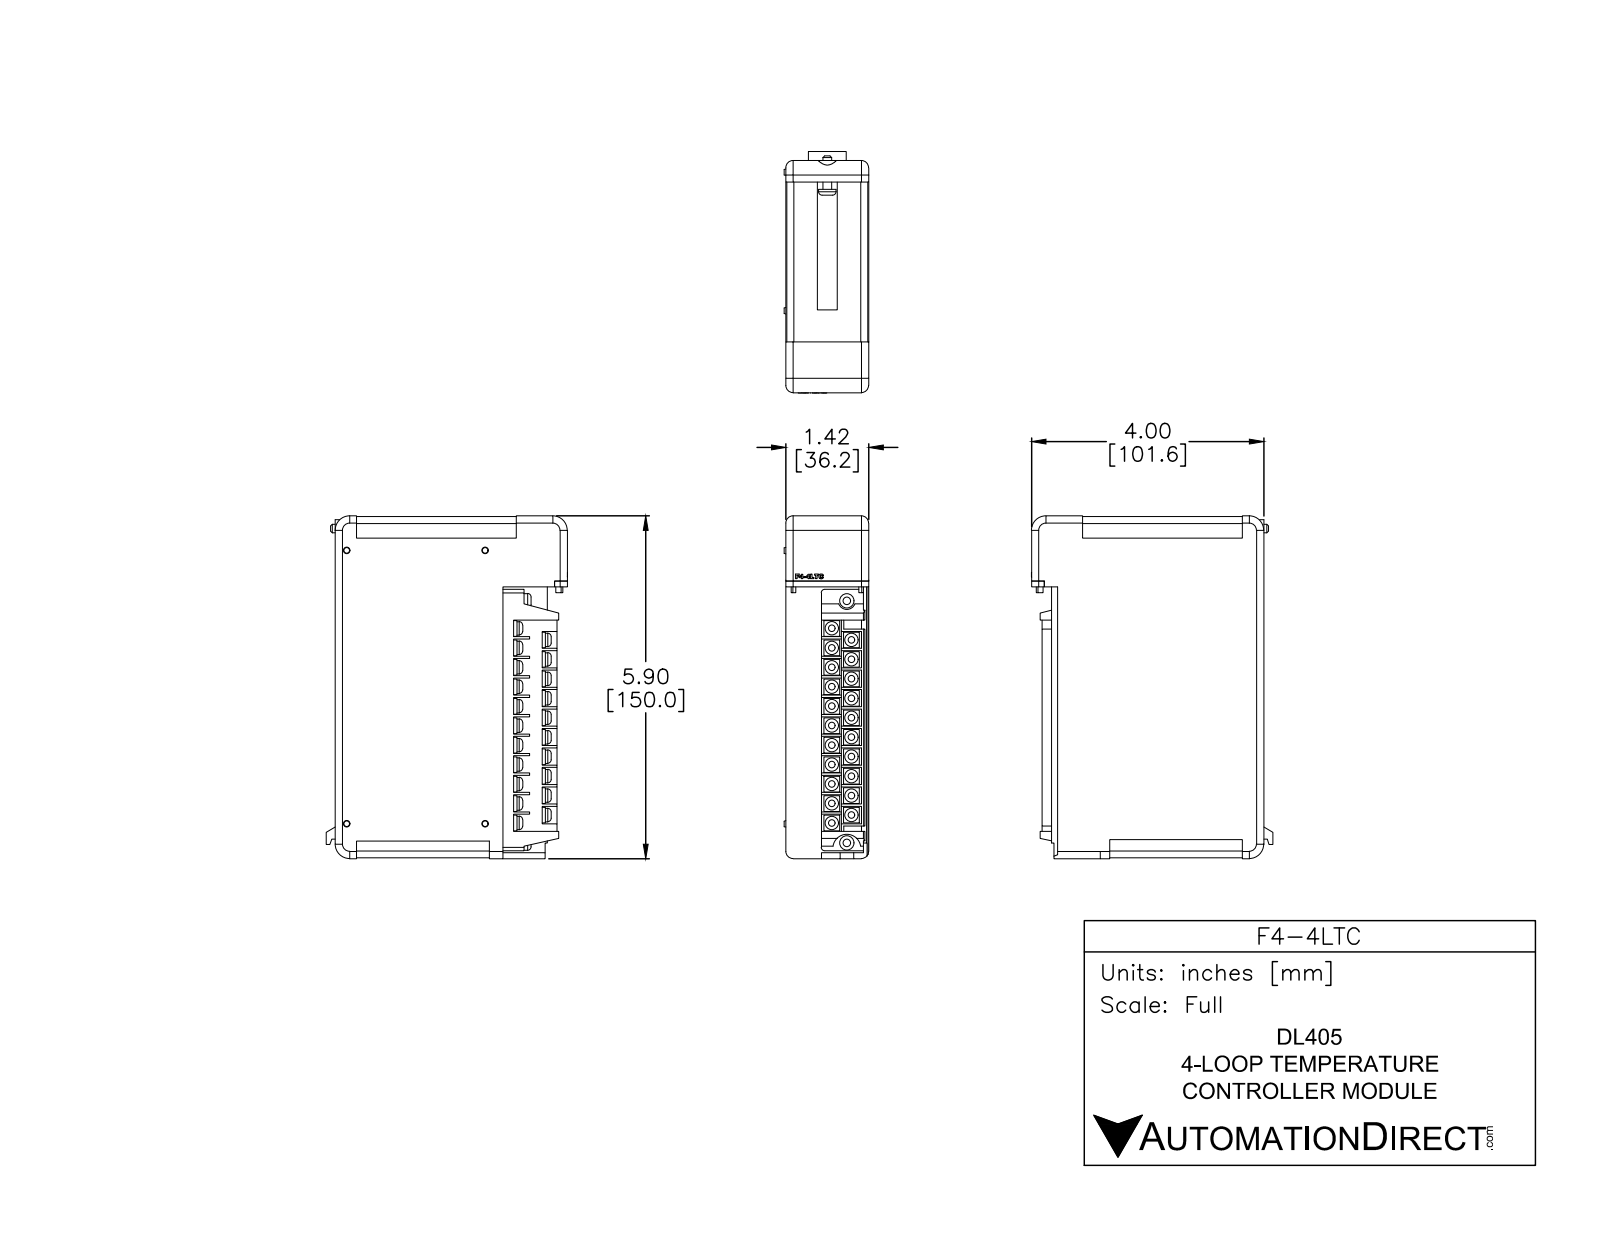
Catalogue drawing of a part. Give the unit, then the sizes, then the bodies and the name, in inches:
Units: inches
Overall size (bounding box): 5.905 × 4.156 × 1.455
Round bosses / shafts (diameter × count): ⌀0.23 ×21, ⌀0.25 ×2, ⌀0.3 ×1, ⌀0.15 ×1
Partial cylindrical surfaces — rounded edges, fillets, slot ends (radius × count): R0.125 ×8, R0.12 ×4, R0.25 ×3, R0.015 ×2, R0.03 ×2, R0.06 ×2, R0.149 ×1, R0.151 ×1
Main face-to-face distances: 1.425, 0.015, 2.89, 5.875, 1.41, 0.47, 0.2, 0.955, 5.89, 1.21
Volume: 27.51 in³ · Surface area: 86.81 in²
Bodies: 13 solids, 576 faces (418 planar, 86 cylindrical, 72 other)
Part name (STEP PRODUCT): F4--4LTC
STEP written by: SolidWorks 2014 (AUTOMOTIVE_DESIGN)
